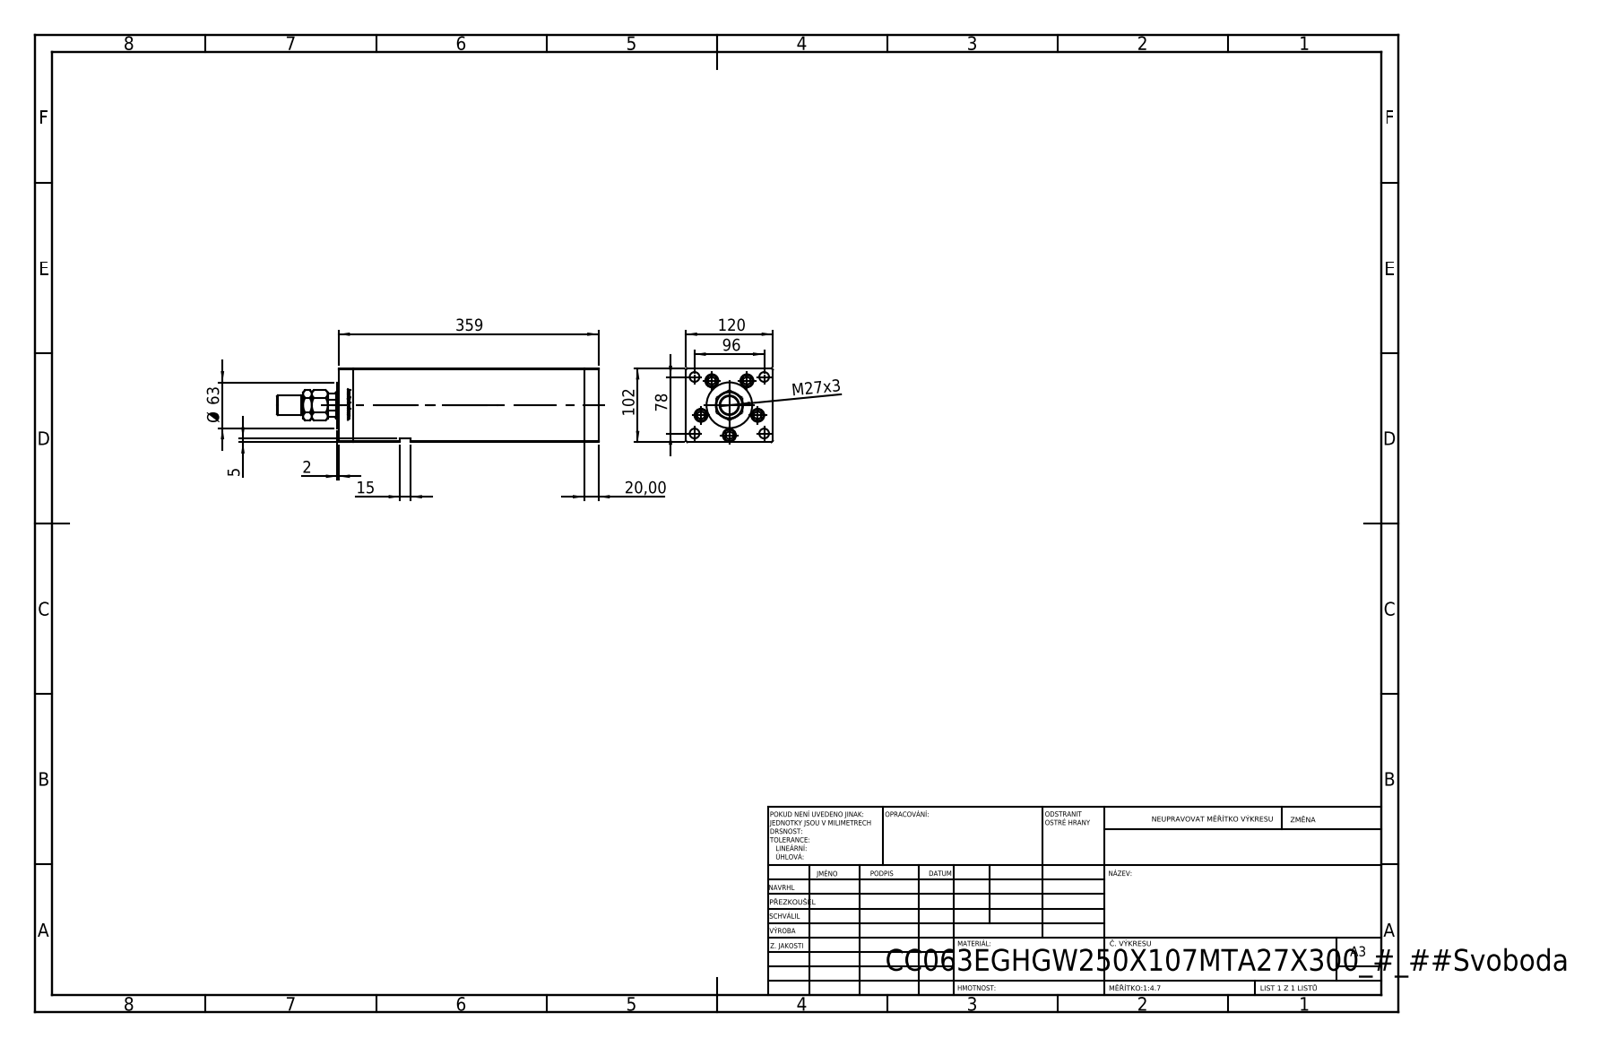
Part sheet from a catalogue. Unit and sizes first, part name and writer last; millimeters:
Units: millimetres
Overall size (bounding box): 443.5 × 120 × 102
Round holes (diameter × count): ⌀13.5 ×9, ⌀18 ×5, ⌀12.5 ×4, ⌀18.5 ×4, ⌀2 ×2, ⌀13.16 ×2, ⌀25.5 ×1, ⌀36 ×1, ⌀37.5 ×1
Round bosses / shafts (diameter × count): ⌀17 ×5, ⌀8 ×5, ⌀63 ×1, ⌀27 ×1, ⌀25 ×1
Partial cylindrical surfaces — rounded edges, fillets, slot ends (radius × count): R0.93 ×2, R17.5 ×1
Main face-to-face distances: 120, 102, 20, 318.5, 338.5, 34.25, 358.5, 14.25, 304.25, 324.25
Hole centre spacings: 41.5, 61.85, 24.39, 26.69, 47.92, 48.07, 49.84, 53.57
Volume: 3 720 000 mm³ · Surface area: 415 514 mm²
Bodies: 15 solids, 1263 faces (490 planar, 169 cylindrical, 604 other)
Part name (STEP PRODUCT): MTA; V220C_VC_E; ALLEN BOLT; V220C BACK_E (+2 more)
STEP written by: SolidWorks 2019 (CONFIG_CONTROL_DESIGN)
